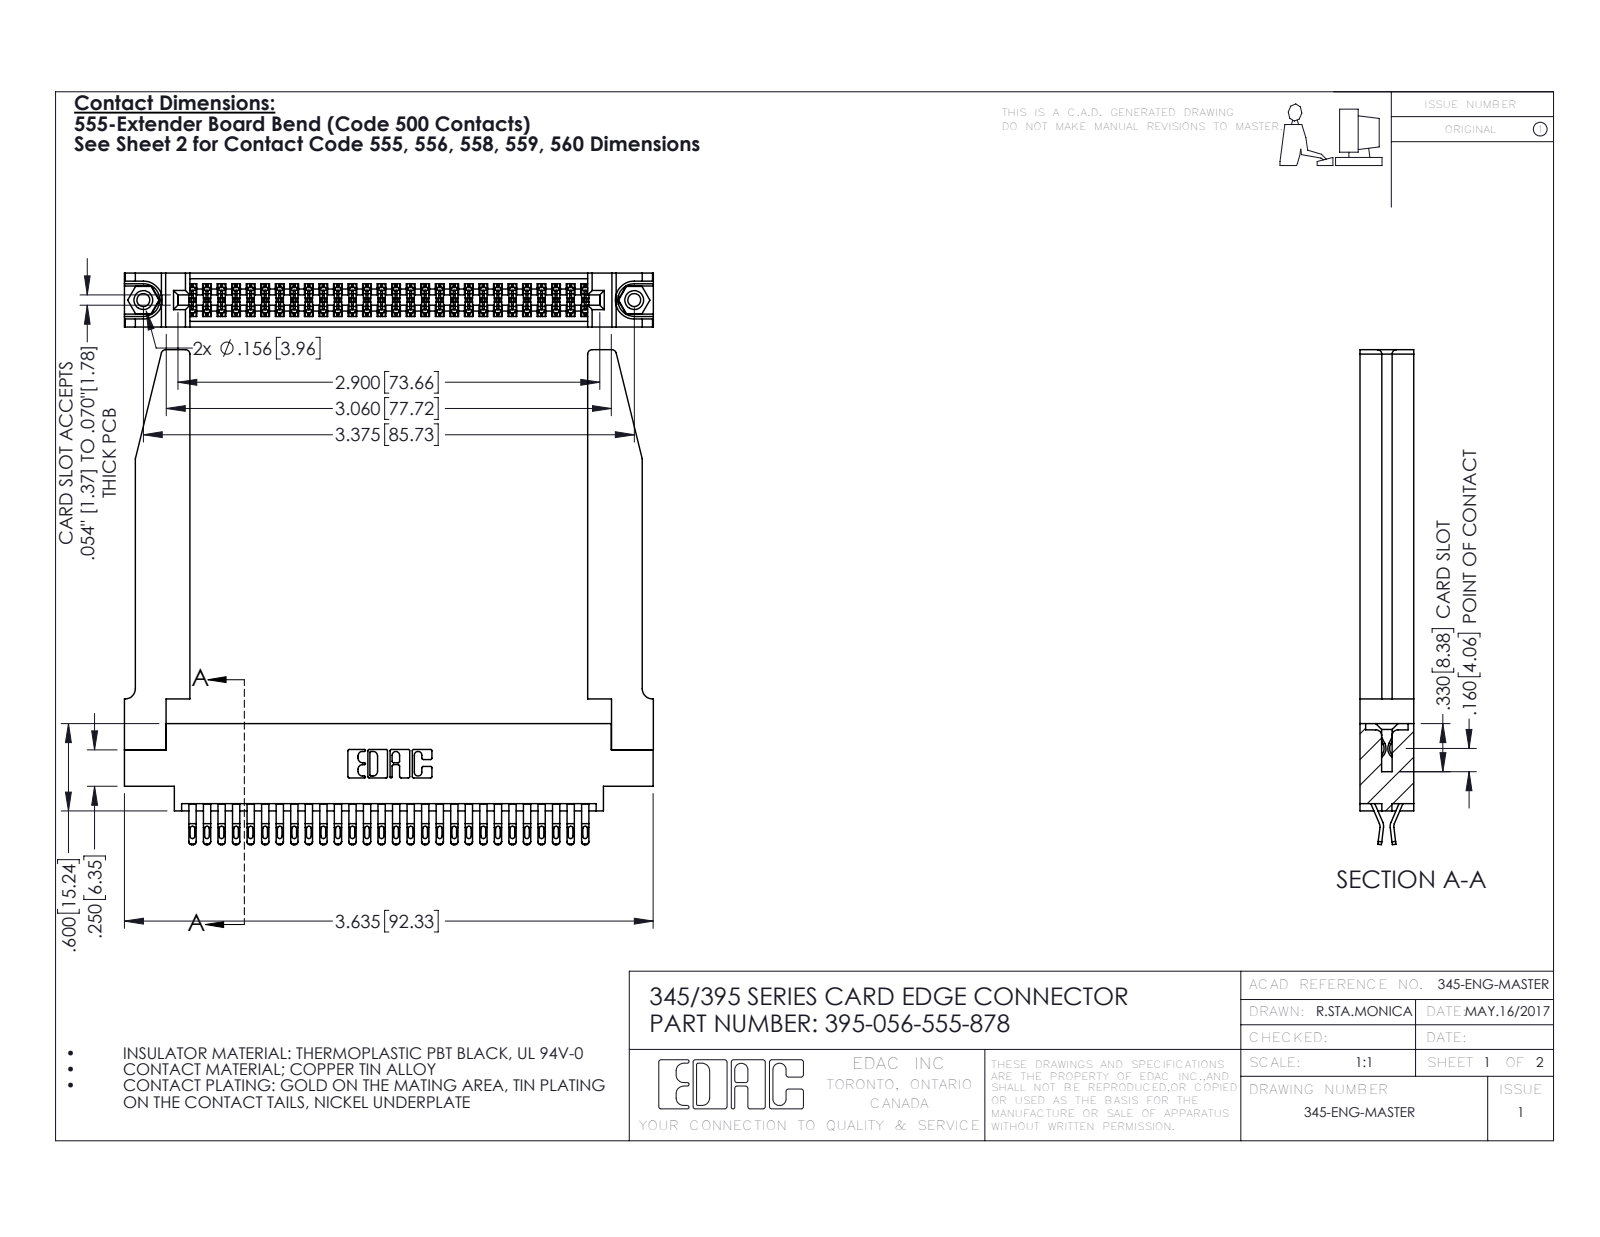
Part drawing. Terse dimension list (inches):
name: 345-292-001_555 Tail; 345-220-078_345-220-078; 395-056-555-878; 345-250-001_345-250-001-102 (+1 more)
written by: SolidWorks 2016 (CONFIG_CONTROL_DESIGN)
unit: in
bodies: 61 solids, 3500 faces (1962 planar, 1486 cylindrical, 52 other)
size: 3.636 × 3.402 × 0.37
volume: 1.017 in³; area: 31.65 in²
holes: 2× ⌀0.089, 2× ⌀0.125, 2× ⌀0.156, 1× ⌀0.064
bosses: 2× ⌀0.155
rounds: 140× R0.016, 112× R0.02, 84× R0.006, 22× R0.01, 8× R0.03, 6× R0.007, 6× R0.031, 3× R0.026
face distances: 0.37, 0.072, 0.298, 0.025, 0.098, 0.272, 0.2, 0.225, 0.148, 0.15
hole spacings: 0.27, 3.14, 3.375
